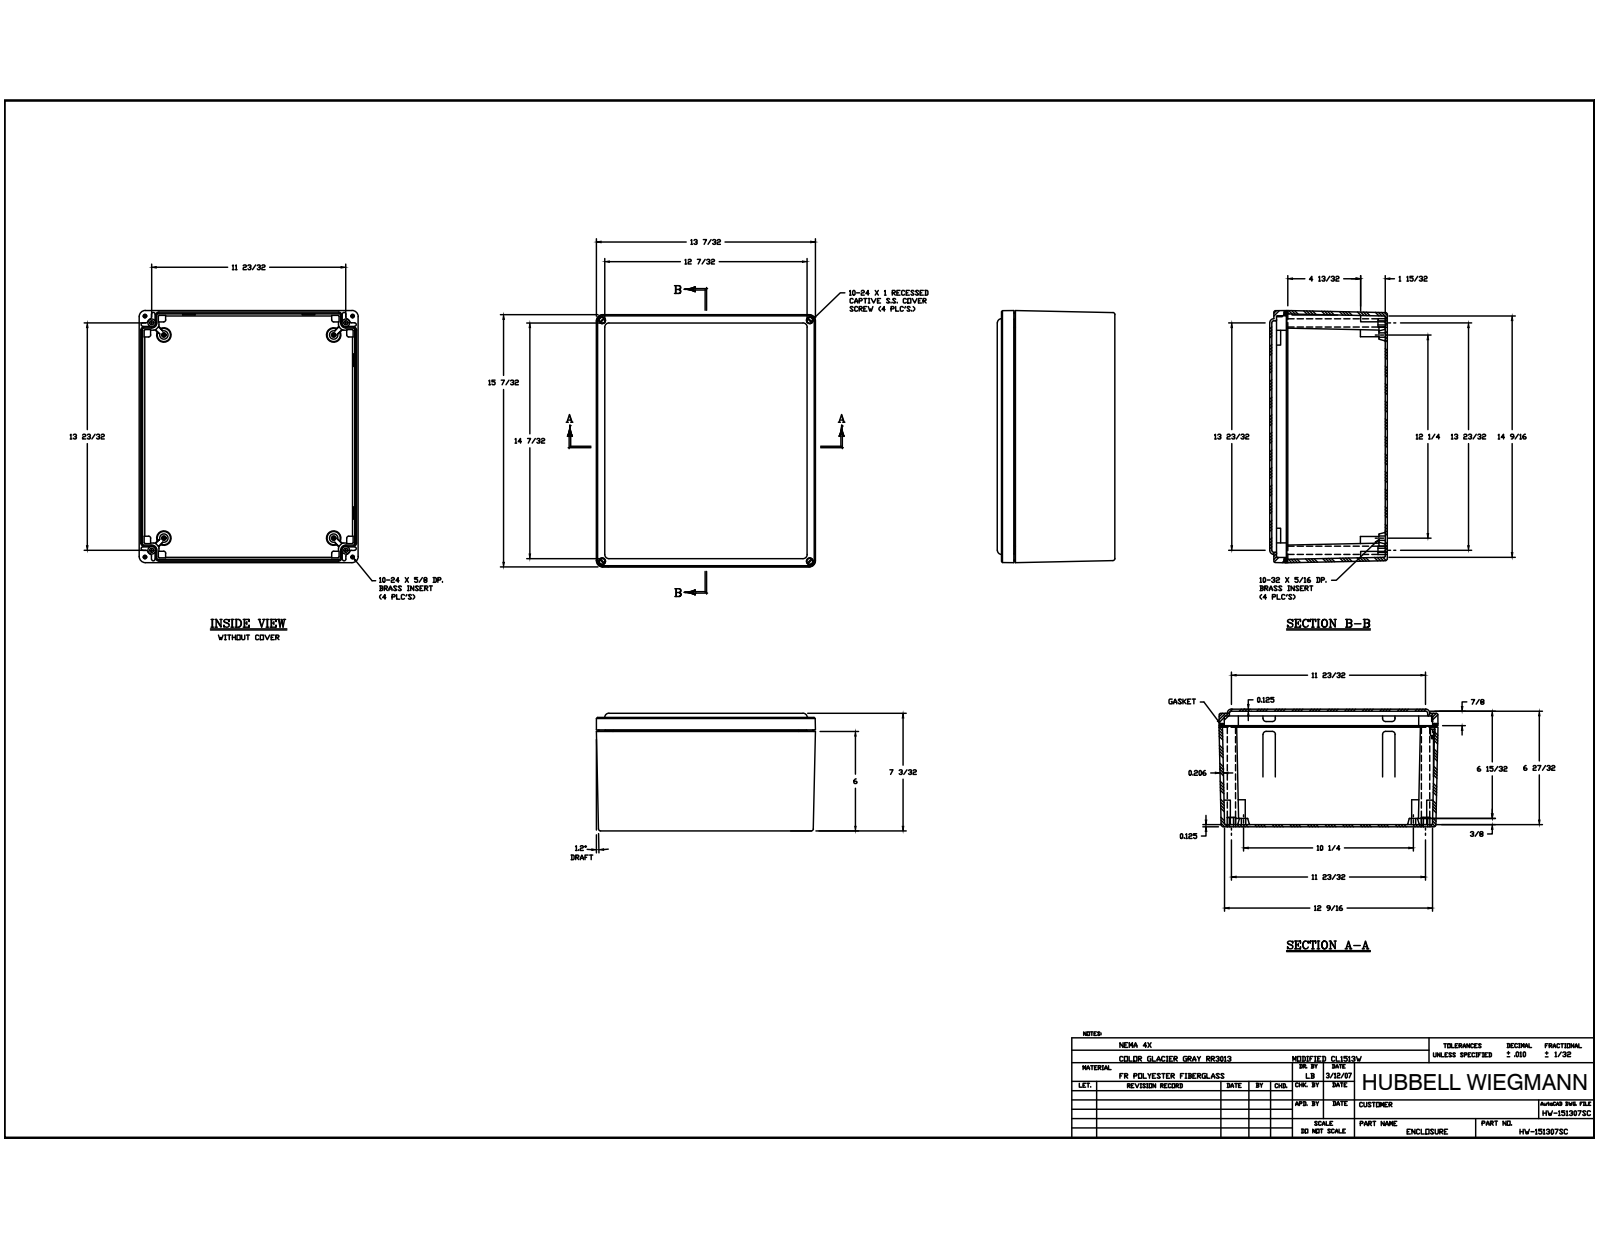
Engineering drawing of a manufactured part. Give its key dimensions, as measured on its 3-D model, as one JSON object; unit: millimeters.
{"part_name": "WP1513WBOX; 0.3125-18 X 0.563 DP BRASS INSERT; 10-32 X0.3125 DP BRASS INSERT; 10-24 X 0.625 DP BRASS INSERT (+5 more)", "step_written_by": "Autodesk Inventor 2014 (AUTOMOTIVE_DESIGN)", "units": "millimeters", "bodies": {"solids": 24, "faces": 1128, "planar": 453, "cylindrical": 307, "other": 368}, "overall_size": [386.59, 335.79, 180.19], "volume_mm3": 2276000, "surface_area_mm2": 1081000, "round_holes": [[7.14, 8], [3.68, 4], [3.96, 4], [3.97, 4], [4.83, 4], [5.56, 4], [5.84, 4], [7.11, 4], [7.94, 4], [10.32, 4], [13.49, 4]], "round_bosses_or_shafts": [[9.52, 4], [9.24, 4], [4.86, 4]], "partial_cylinders_radius": [[0.79, 57], [3.17, 40], [1.59, 29], [0.25, 16], [1.5, 8], [4.76, 8], [4.78, 8], [6.35, 8]], "face_to_face_distances": [4.72, 3.17, 173.84, 180.19, 177.02, 3.18, 177.01, 6.35, 170.67, 19.05], "hole_center_spacings": [14.57, 14.58, 26.39, 40.96, 40.97, 279.66, 290.79, 290.8]}
